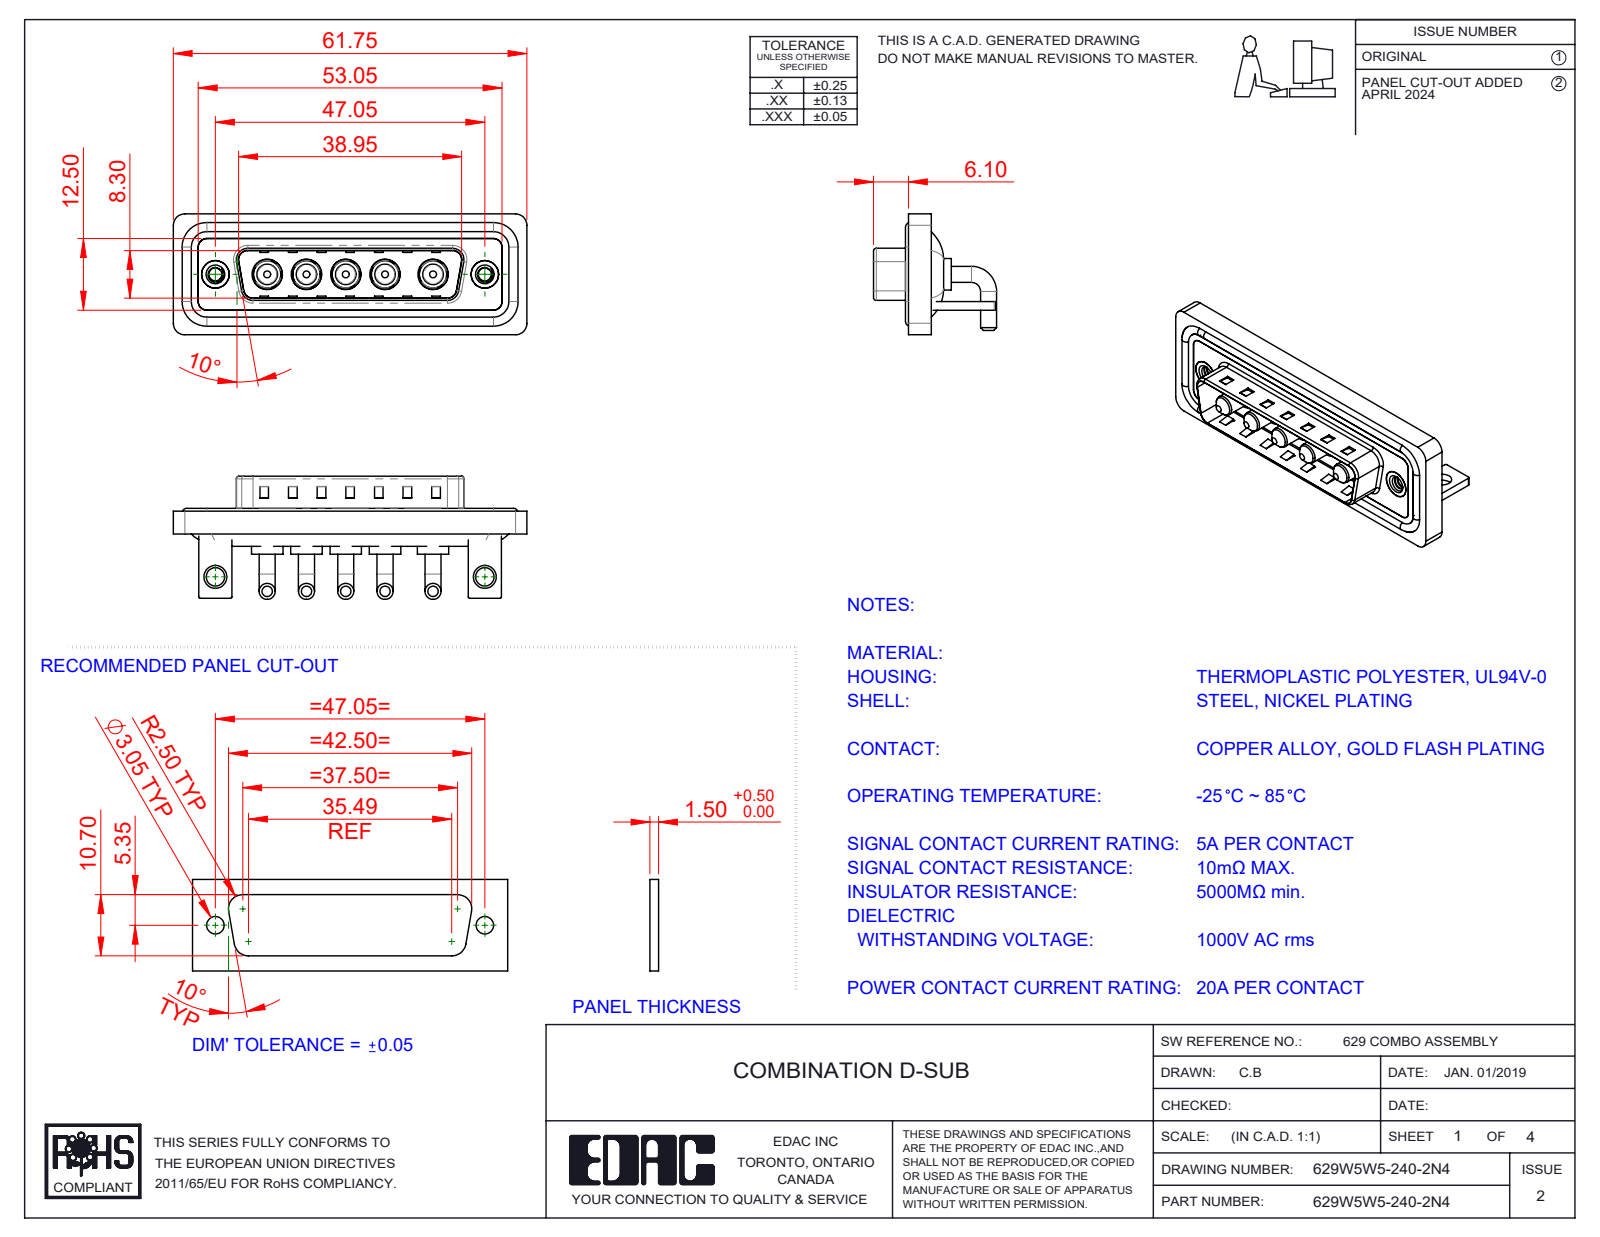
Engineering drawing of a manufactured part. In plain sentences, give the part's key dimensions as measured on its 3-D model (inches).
The part is named "629Combo Shell Front_25 Contacts; 629Combo Threaded Rivet_3; 629Combo Housing_5W5; Power Pin_20A RA (+4 more)". Its 3-D file was written by "SolidWorks 2023 (CONFIG_CONTROL_DESIGN)". It is 19 solids with 738 faces: 279 planar, 311 cylindrical and 148 other. Overall it measures 2.431 by 0.846 by 0.831 inches. Its volume is 0.493 cubic inches and its surface area 19.93 square inches. Round holes: 5 of diameter 0.191, 5 of diameter 0.209, 2 of diameter 0.089, 2 of diameter 0.126, 2 of diameter 0.157, 2 of diameter 0.189, 2 of diameter 0.197. Round bosses or shafts: 10 of diameter 0.11, 5 of diameter 0.217, 5 of diameter 0.205, 5 of diameter 0.187, 5 of diameter 0.148, 5 of diameter 0.142, 4 of diameter 0.063, 2 of diameter 0.193. Partial cylindrical surfaces (rounded edges, fillets, slot ends): 19 of radius 0.079, 18 of radius 0.059, 16 of radius 0.01, 9 of radius 0.02, 8 of radius 0.063, 5 of radius 0.083, 4 of radius 0.024, 4 of radius 0.026. The main face-to-face distances are 0.016, 0.059, 0.114, 0.031, 0.083, 0.043, 0.146, 0.177, 0.161, 0.047. The hole center spacings are 0.27, 0.541, 1.852, 0.27, 0.27, 0.33, 0.33, 0.356.
